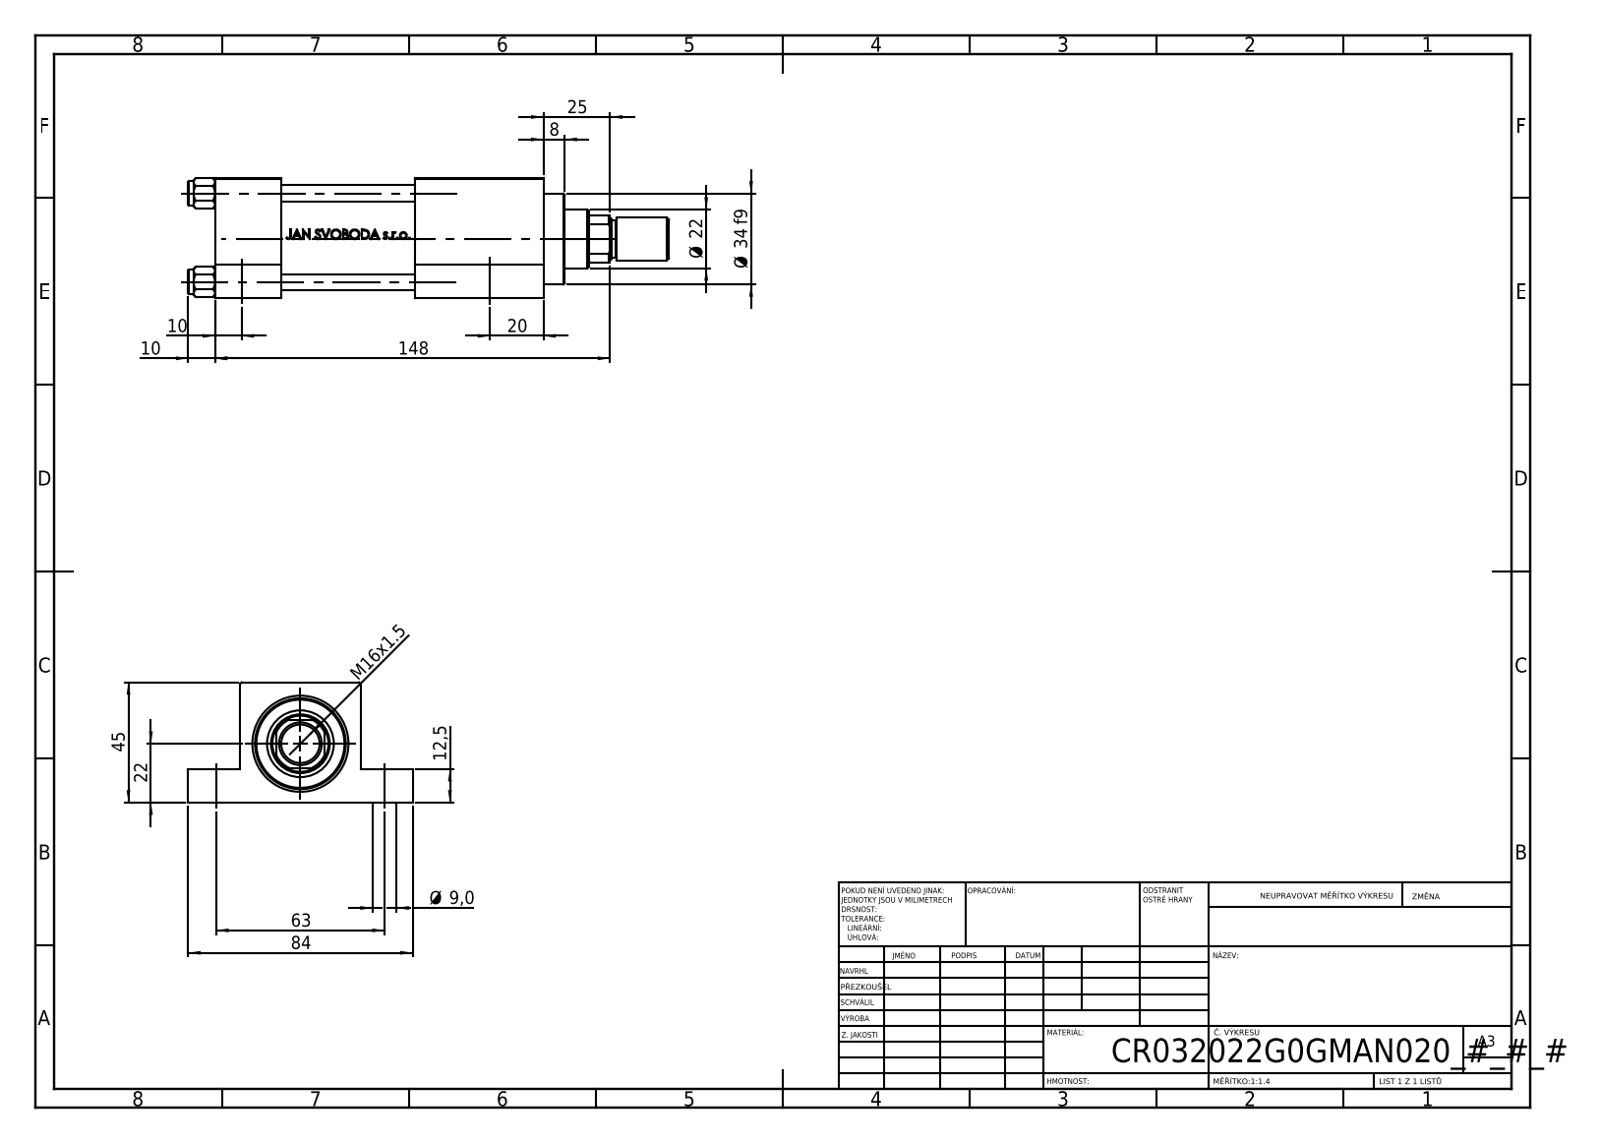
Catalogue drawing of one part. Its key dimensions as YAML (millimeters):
part_name: "V215CR_G_TYCINKA; V215CR_G_Body; ROD_END_AH; V215_VC_A (+2 more)"
step_written_by: "SolidWorks 2019 (CONFIG_CONTROL_DESIGN)"
units: millimeters
bodies: {solids: 12, faces: 1100, planar: 434, cylindrical: 128, other: 538}
overall_size: [180, 84, 45]
volume: 248227
surface_area: 80219
round_holes:
  - {diameter: 6, count: 4}
  - {diameter: 9, count: 4}
  - {diameter: 7, count: 2}
  - {diameter: 13.16, count: 2}
  - {diameter: 20, count: 2}
  - {diameter: 10.5, count: 1}
  - {diameter: 22, count: 1}
  - {diameter: 24, count: 1}
  - {diameter: 25, count: 1}
  - {diameter: 32, count: 1}
  - {diameter: 33, count: 1}
round_bosses_or_shafts:
  - {diameter: 9, count: 4}
  - {diameter: 38, count: 1}
  - {diameter: 34, count: 1}
  - {diameter: 16, count: 1}
  - {diameter: 14, count: 1}
partial_cylinders:
  - {radius: 10.5, count: 1}
face_to_face_distances: [45, 25, 12.5, 32.5, 123, 19.5, 64.5, 98, 50, 75]
hole_center_spacings: [33.2, 23.13, 23.83, 46.95, 63, 93, 112.33, 75.5]
